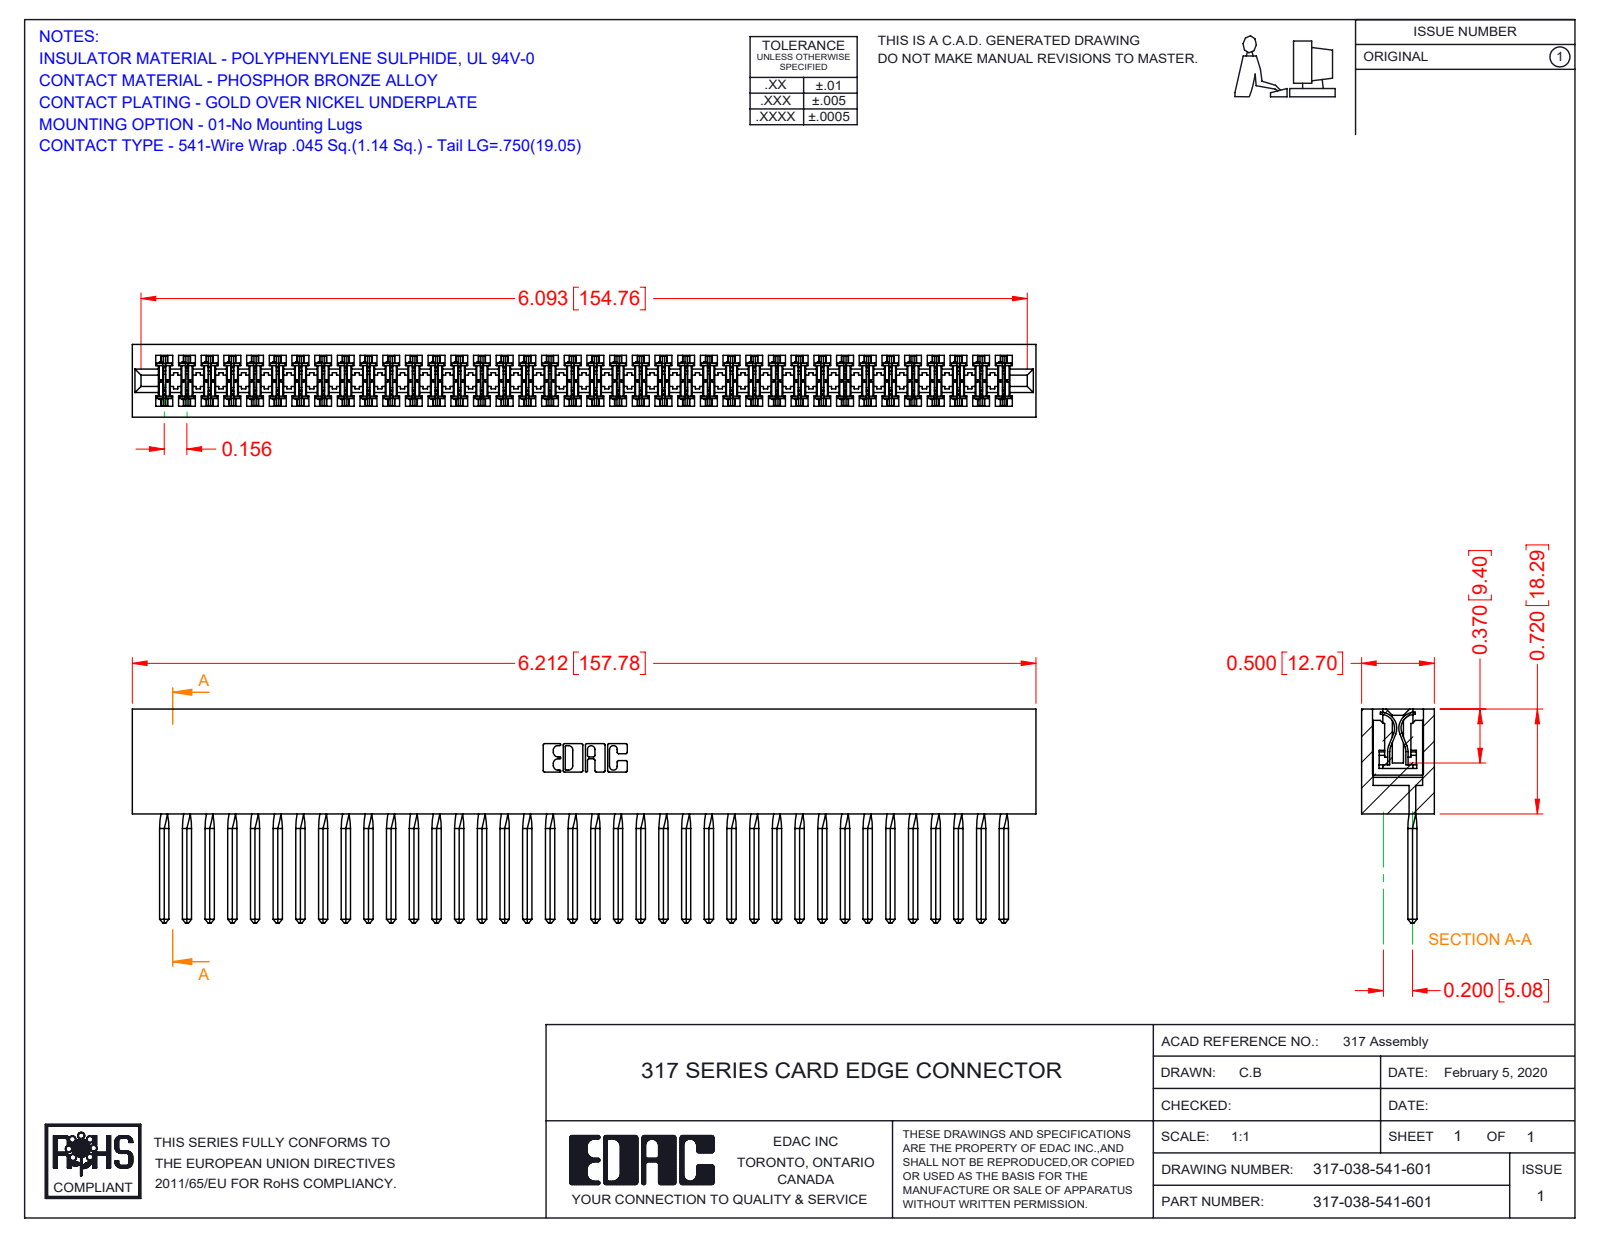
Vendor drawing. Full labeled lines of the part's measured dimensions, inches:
Part name (STEP PRODUCT): 317-290-002_541; 317 Part_Lugless; 317-038-541-601
STEP written by: SolidWorks 2016 (CONFIG_CONTROL_DESIGN)
Units: inches
Bodies: 39 solids, 5866 faces (4762 planar, 952 cylindrical, 152 other)
Overall size (bounding box): 6.212 × 1.47 × 0.5
Volume: 1.658 in³ · Surface area: 59.6 in²
Partial cylindrical surfaces — rounded edges, fillets, slot ends (radius × count): R0.015 ×76, R0.01 ×22, R0.007 ×6, R0.031 ×6, R0.026 ×3, R0.095 ×2, R0.1 ×2, R0.11 ×2
Main face-to-face distances: 0.075, 0.5, 0.425, 0.35, 0.195, 0.11, 0.72, 0.115, 0.211, 0.289
